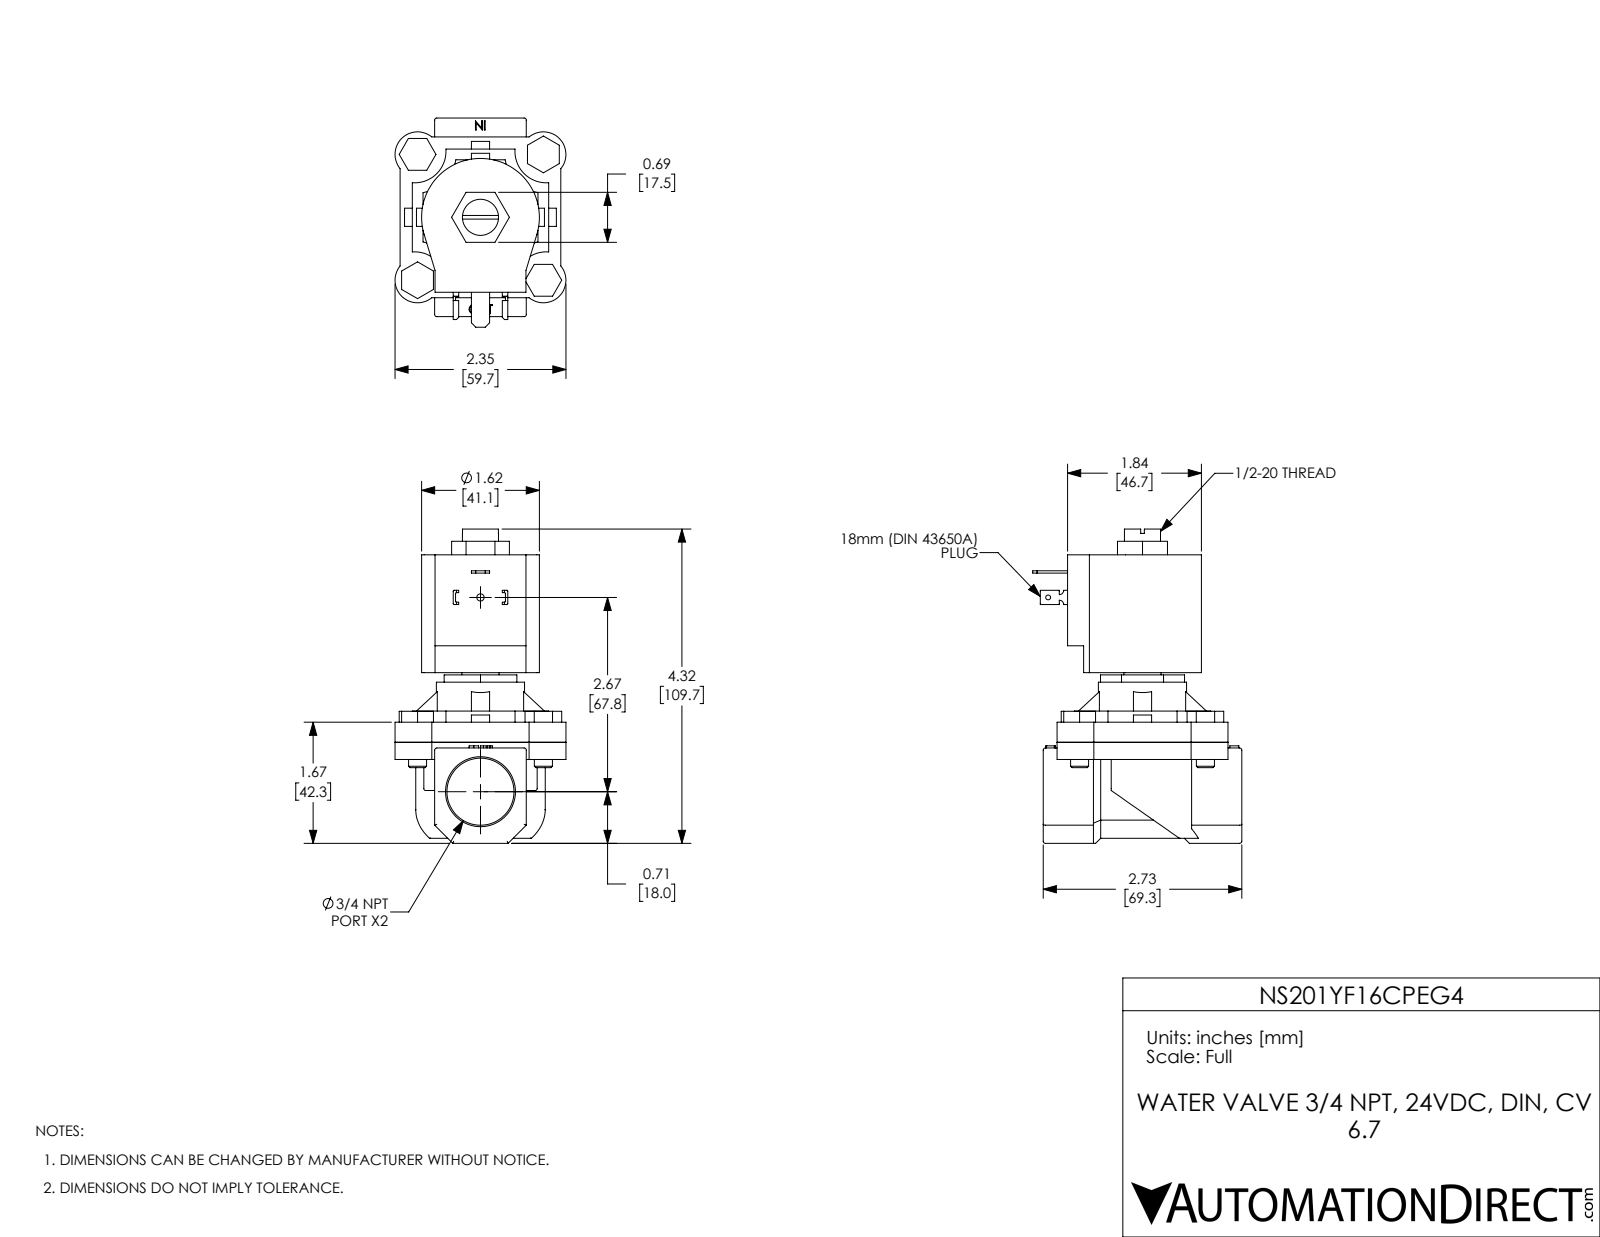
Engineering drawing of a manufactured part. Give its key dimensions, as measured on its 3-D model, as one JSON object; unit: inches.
{"part_name": "NS201YF16CPEG5", "step_written_by": "SolidWorks 2021 (CONFIG_CONTROL_DESIGN)", "units": "inches", "bodies": {"solids": 11, "faces": 387, "planar": 241, "cylindrical": 113, "other": 33}, "overall_size": [4.32, 2.875, 2.35], "volume_in3": 10.62, "surface_area_in2": 70.92, "round_holes": [[0.25, 4], [0.067, 1], [0.1, 1], [0.496, 1], [0.512, 1], [0.922, 1], [1.155, 1]], "round_bosses_or_shafts": [[0.248, 4], [1.213, 1]], "partial_cylinders_radius": [[0.03, 15], [0.015, 8], [0.31, 4], [0.432, 4], [0.579, 4], [0.06, 2], [0.81, 1], [0.89, 1]], "face_to_face_distances": [0.276, 2.577, 2.301, 0.236, 0.512, 2.813, 0.475, 1.735, 1.26, 2.21], "hole_center_spacings": [1.223, 1.73, 2.446, 2.67]}
